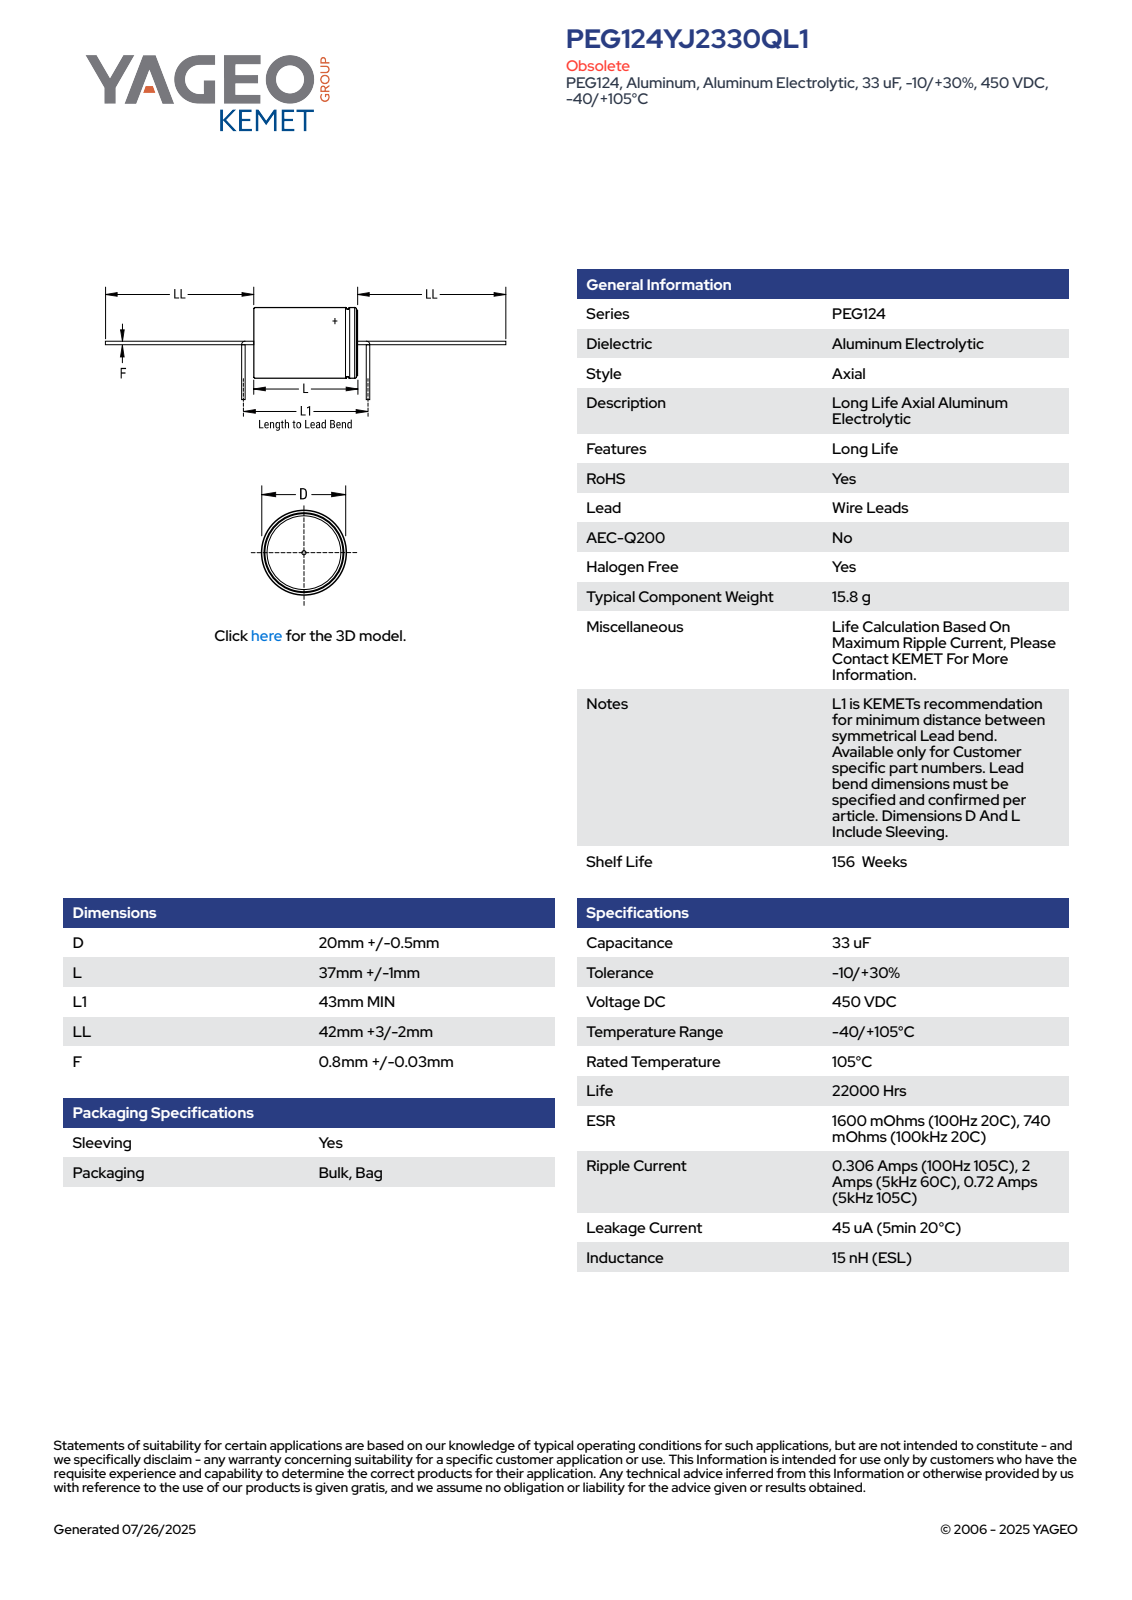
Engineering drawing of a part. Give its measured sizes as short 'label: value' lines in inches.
name: CAA_PEG124_20X37_D20.5L38LL45F0.83
written by: SolidWorks 2014 (AUTOMOTIVE_DESIGN)
unit: in
bodies: 1 solid, 99 faces (27 planar, 29 cylindrical, 43 other)
size: 4.921 × 0.807 × 0.807
volume: 0.749 in³; area: 5.273 in²
holes: 1× ⌀0.768
bosses: 1× ⌀0.807, 1× ⌀0.787, 1× ⌀0.033
rounds: 1× R0.403
face distances: 1.457, 1.496, 0.039, 1.772, 3.228, 3.268, 4.921, 3.15, 1.693, 1.654
